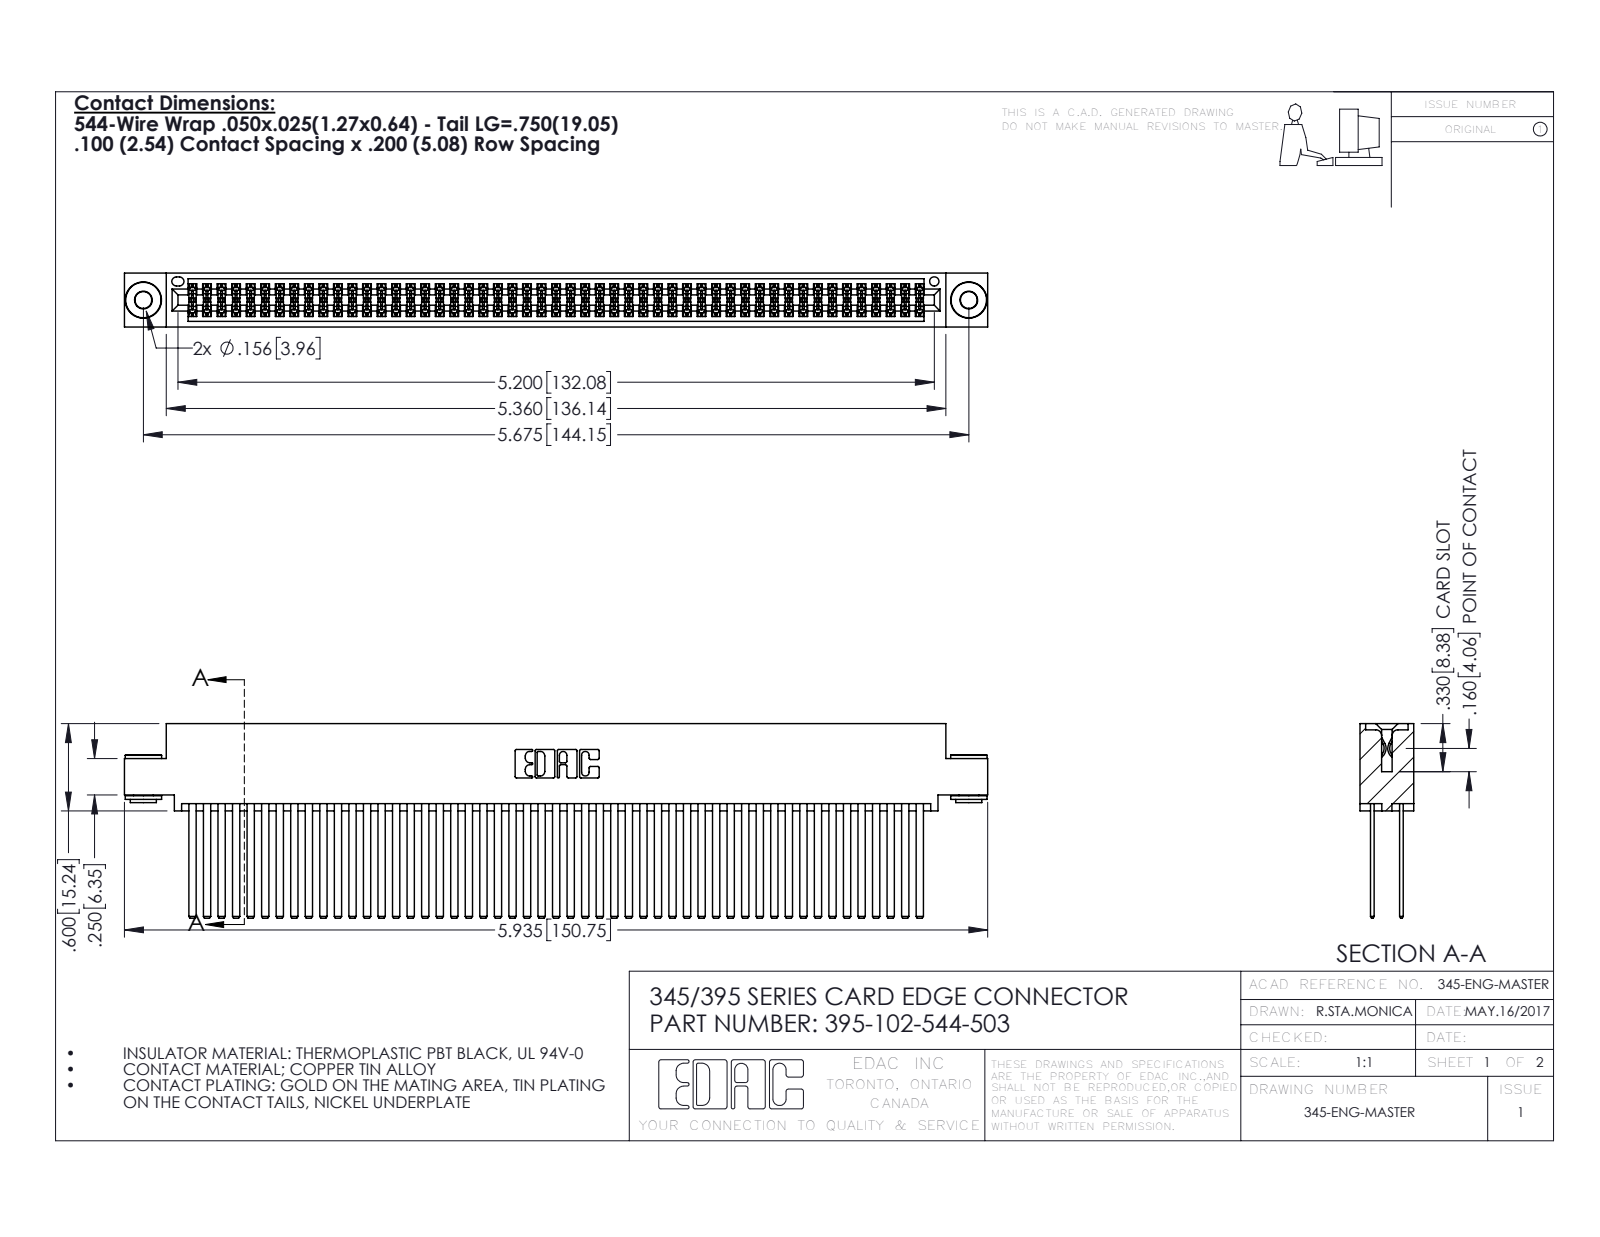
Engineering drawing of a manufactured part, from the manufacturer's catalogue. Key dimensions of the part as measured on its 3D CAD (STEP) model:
Part name (STEP PRODUCT): 345 Part_0.110 Offset - 0.156 Dia-TH; 345-250-002_345-250-002-102; 395-102-544-503; 345-292-001_345-293-144
STEP written by: SolidWorks 2016 (CONFIG_CONTROL_DESIGN)
Units: inches
Bodies: 105 solids, 4656 faces (3052 planar, 1596 cylindrical, 8 other)
Overall size (bounding box): 5.935 × 1.337 × 0.37
Volume: 0.983 in³ · Surface area: 44.12 in²
Round holes (diameter × count): ⌀0.116 ×2, ⌀0.156 ×2, ⌀0.064 ×1
Round bosses / shafts (diameter × count): ⌀0.25 ×2, ⌀0.18 ×2, ⌀0.136 ×2
Partial cylindrical surfaces — rounded edges, fillets, slot ends (radius × count): R0.006 ×153, R0.01 ×22, R0.007 ×6, R0.031 ×6, R0.026 ×3, R0.014 ×2, R0.019 ×2, R0.022 ×2
Main face-to-face distances: 0.2, 0.025, 0.072, 0.098, 0.272, 0.298, 0.225, 0.175, 0.37, 0.05
Hole centre spacings: 0.27, 5.439, 5.675
